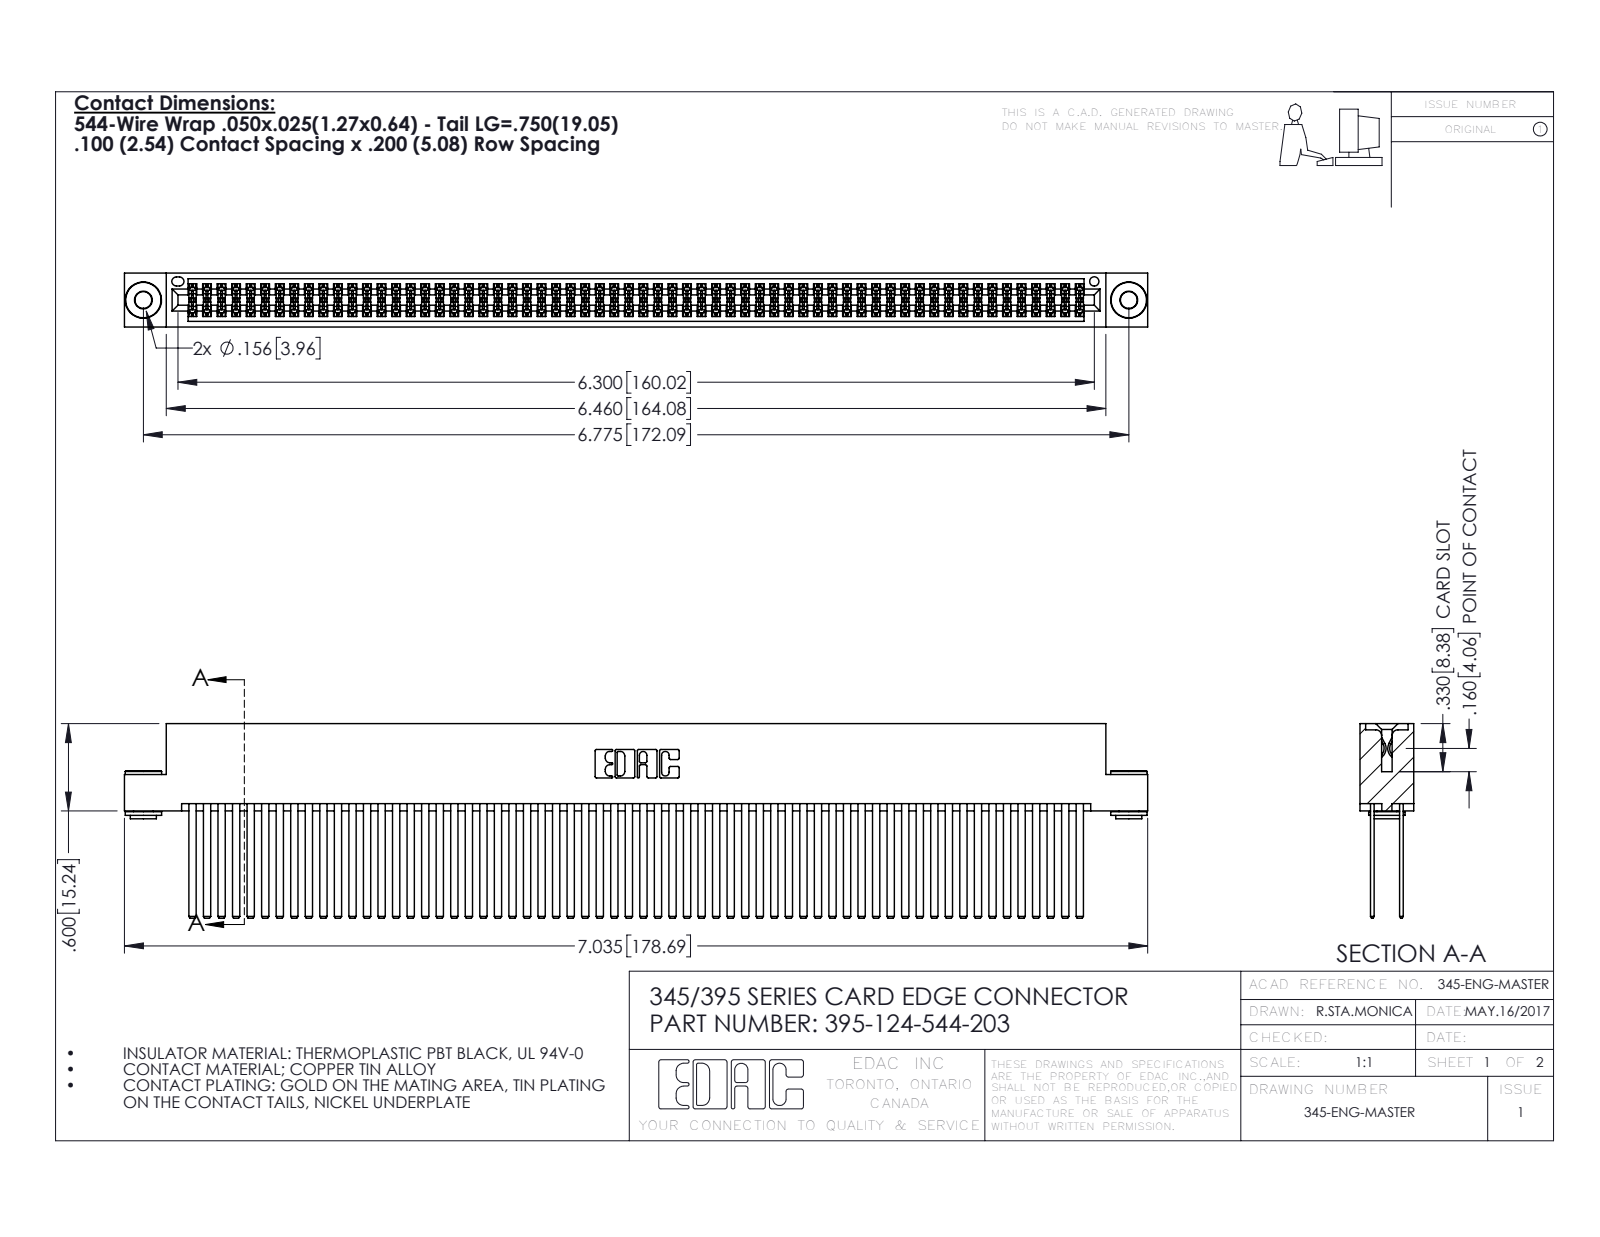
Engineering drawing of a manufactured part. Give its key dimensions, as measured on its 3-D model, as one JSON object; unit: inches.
{"part_name": "345-292-001_345-293-144; 345-250-002_345-250-002-102; 345 Part_Flush Mounting Lugs - 0.156 Dia-TH; 395-124-544-203", "step_written_by": "SolidWorks 2016 (CONFIG_CONTROL_DESIGN)", "units": "inches", "bodies": {"solids": 127, "faces": 5620, "planar": 3686, "cylindrical": 1926, "other": 8}, "overall_size": [7.035, 1.337, 0.37], "volume_in3": 1.178, "surface_area_in2": 53.04, "round_holes": [[0.116, 2], [0.156, 2], [0.064, 1]], "round_bosses_or_shafts": [[0.25, 2], [0.18, 2], [0.136, 2]], "partial_cylinders_radius": [[0.006, 186], [0.01, 22], [0.007, 6], [0.031, 6], [0.026, 3], [0.014, 2], [0.019, 2], [0.022, 2]], "face_to_face_distances": [0.2, 0.025, 0.072, 0.098, 0.272, 0.298, 0.225, 0.175, 0.37, 0.05], "hole_center_spacings": [0.27, 6.539, 6.775]}
